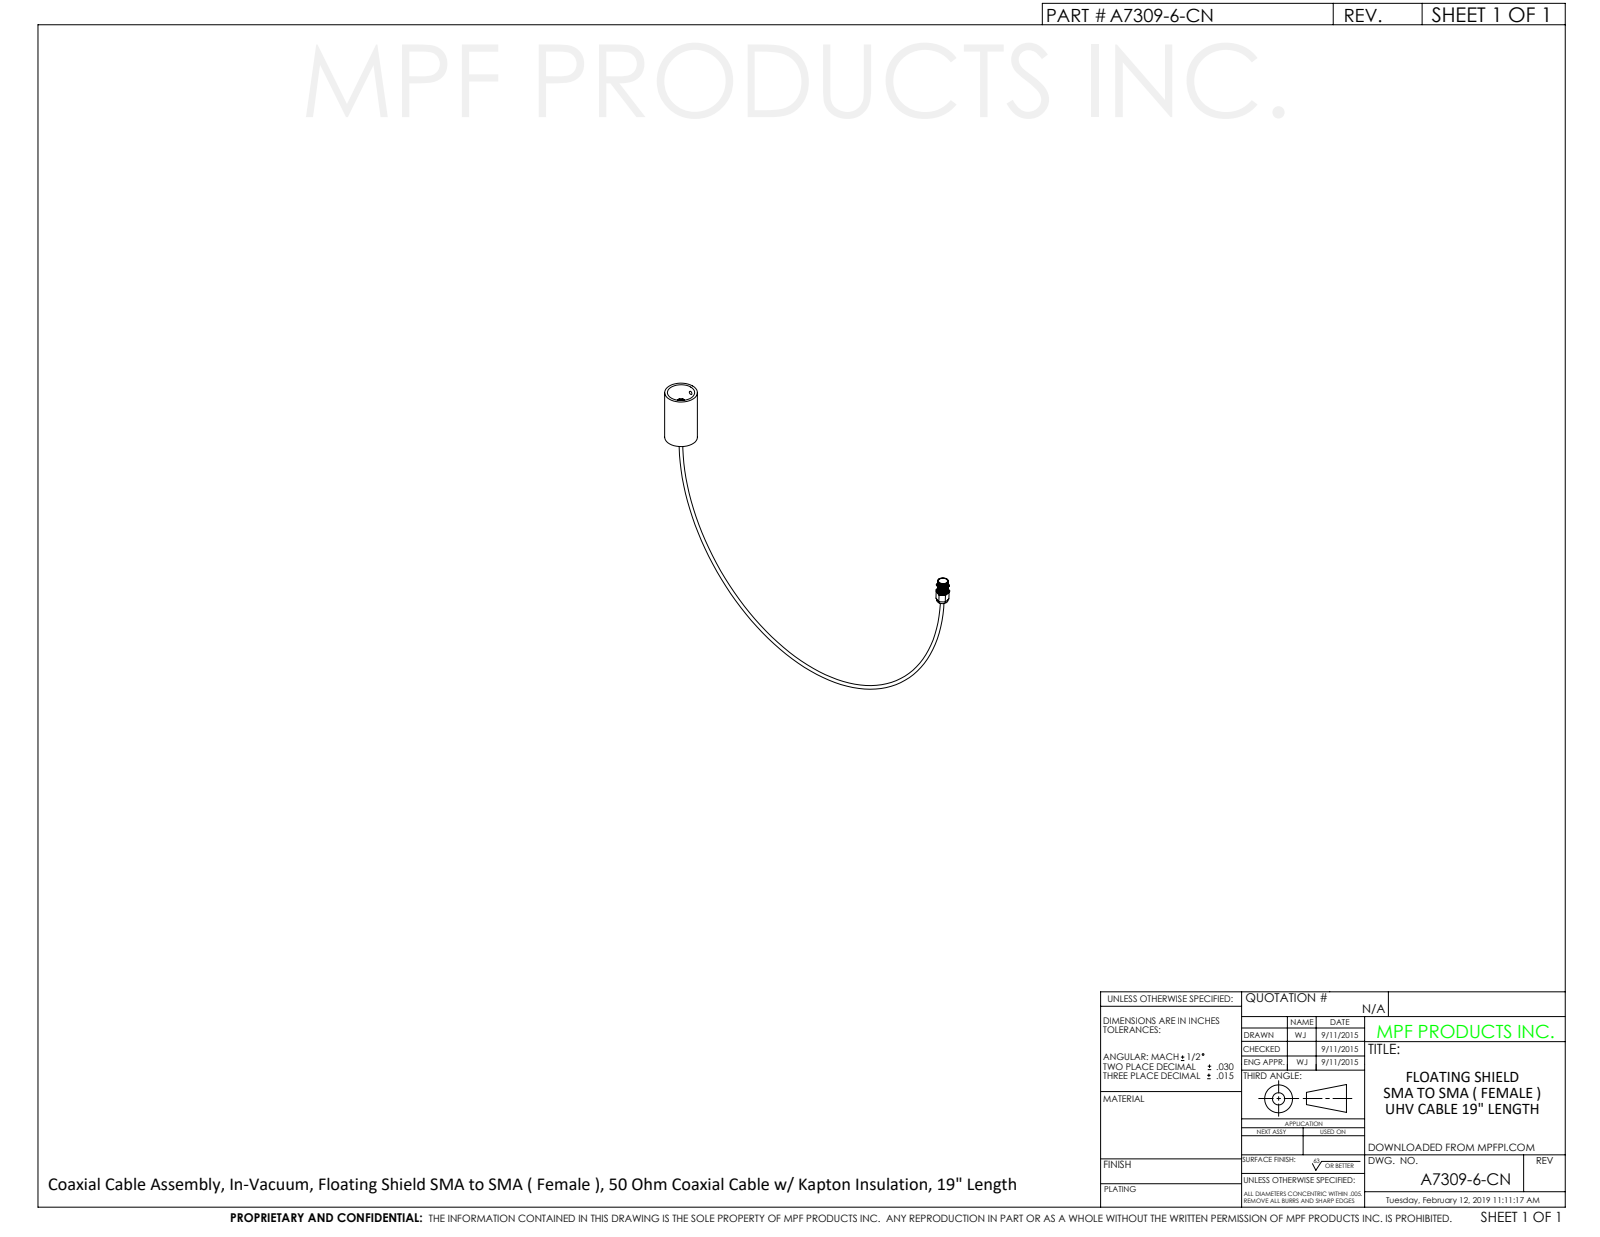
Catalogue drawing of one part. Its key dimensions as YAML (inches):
part_name: "A7309-6-CN; A7300 FEMALE SMA PART; A7309-1-CN_110183"
step_written_by: "SolidWorks 2012 (CONFIG_CONTROL_DESIGN)"
units: inches
bodies: {solids: 4, faces: 213, planar: 76, cylindrical: 56, other: 81}
overall_size: [10.85, 6.833, 1]
volume: 1.013
surface_area: 15.63
round_holes:
  - {diameter: 0.1, count: 3}
  - {diameter: 0.05, count: 1}
  - {diameter: 0.167, count: 1}
  - {diameter: 0.186, count: 1}
  - {diameter: 0.2, count: 1}
  - {diameter: 0.251, count: 1}
  - {diameter: 0.257, count: 1}
  - {diameter: 0.293, count: 1}
  - {diameter: 0.75, count: 1}
round_bosses_or_shafts:
  - {diameter: 1, count: 1}
  - {diameter: 0.307, count: 1}
  - {diameter: 0.294, count: 1}
  - {diameter: 0.25, count: 1}
  - {diameter: 0.207, count: 1}
  - {diameter: 0.2, count: 1}
  - {diameter: 0.18, count: 1}
  - {diameter: 0.165, count: 1}
face_to_face_distances: [1.5, 0.308, 0.04, 0.219, 0.294, 0.12, 0.328, 0.25, 0.214, 0.224]
hole_center_spacings: [0.35]
